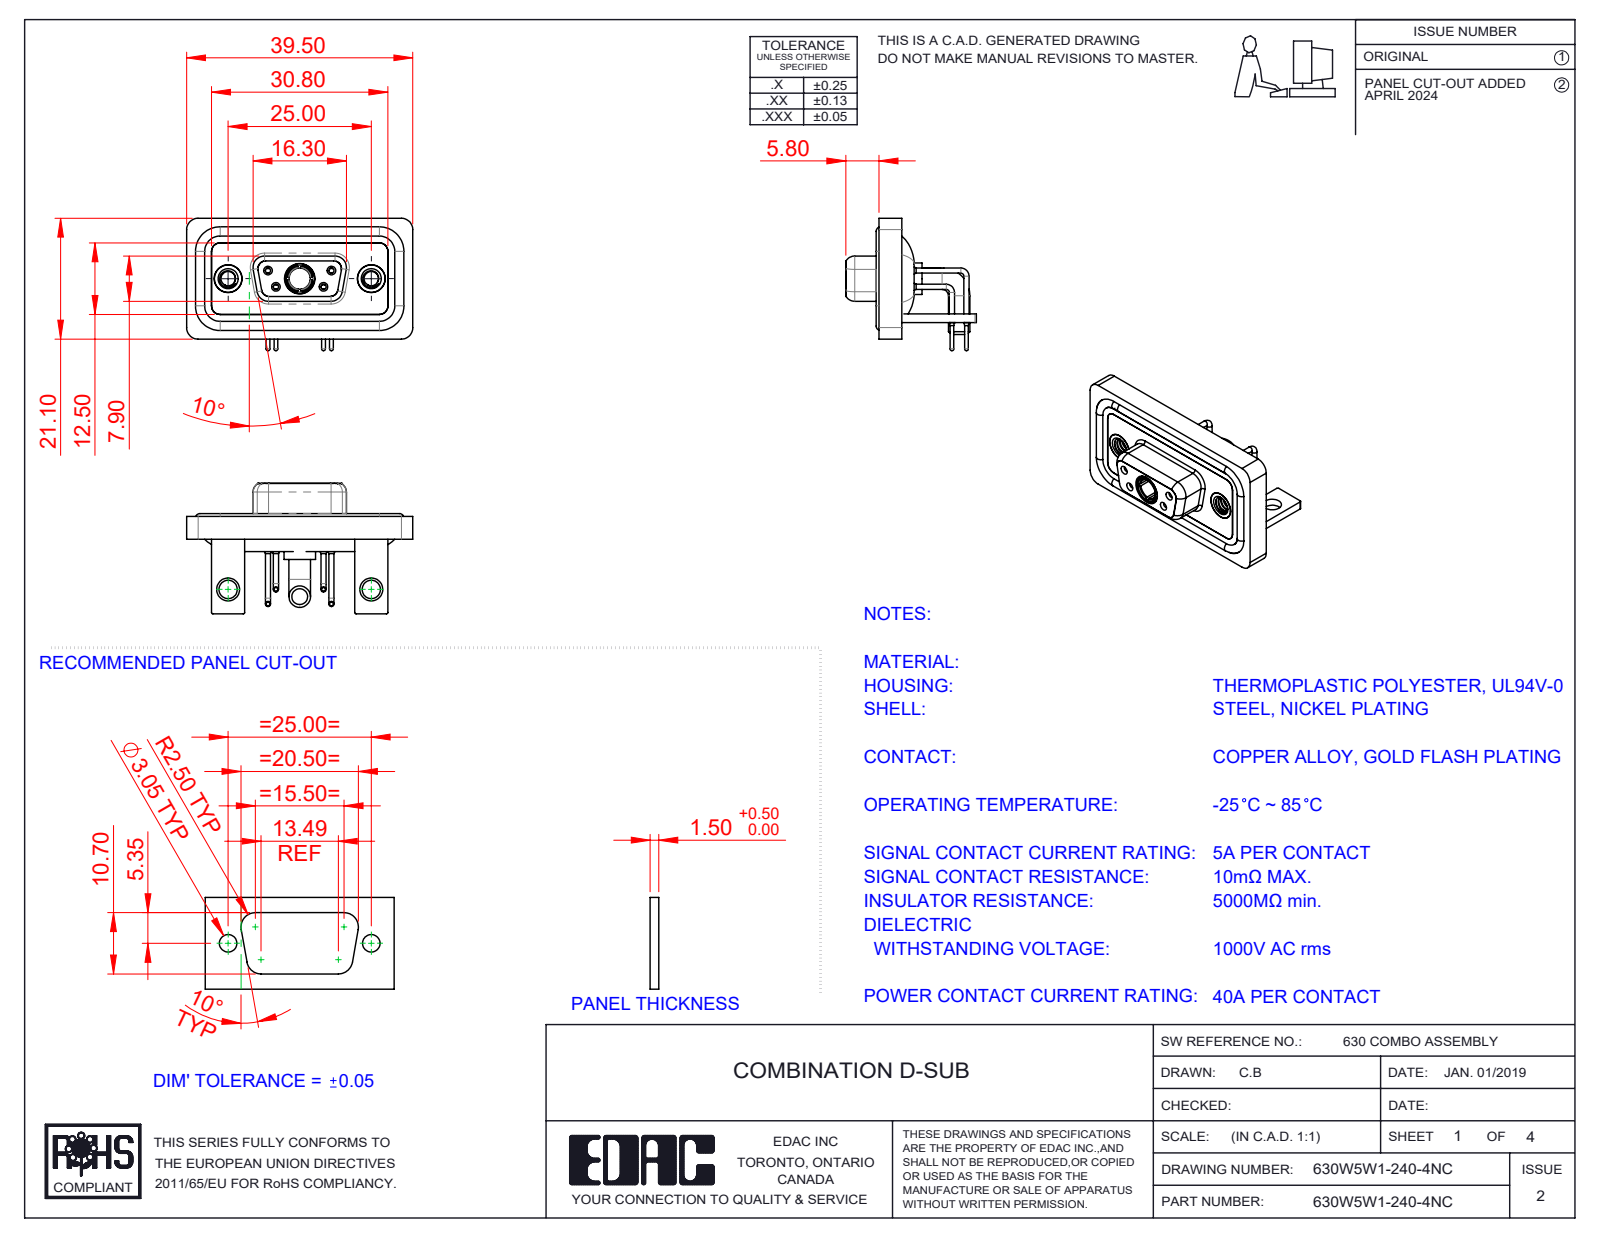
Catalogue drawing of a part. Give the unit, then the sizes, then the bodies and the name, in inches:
Units: inches
Overall size (bounding box): 1.555 × 0.91 × 0.898
Round holes (diameter × count): ⌀0.035 ×4, ⌀0.043 ×4, ⌀0.059 ×4, ⌀0.079 ×4, ⌀0.191 ×3, ⌀0.063 ×2, ⌀0.067 ×2, ⌀0.098 ×2, ⌀0.126 ×2, ⌀0.157 ×2, ⌀0.159 ×2, ⌀0.197 ×2
Round bosses / shafts (diameter × count): ⌀0.063 ×6, ⌀0.035 ×4, ⌀0.026 ×4, ⌀0.195 ×2, ⌀0.189 ×2, ⌀0.148 ×2, ⌀0.217 ×1, ⌀0.205 ×1
Partial cylindrical surfaces — rounded edges, fillets, slot ends (radius × count): R0.079 ×19, R0.059 ×18, R0.01 ×16, R0.053 ×8, R0.063 ×8, R0.02 ×5, R0.024 ×4, R0.026 ×4
Main face-to-face distances: 0.016, 0.114, 0.059, 0.071, 0.043, 0.146, 0.063, 0.031, 0.098, 0.122
Hole centre spacings: 0.124, 0.225, 0.28, 0.492, 0.713, 0.984, 0.173, 0.173
Volume: 0.321 in³ · Surface area: 13.37 in²
Bodies: 15 solids, 718 faces (214 planar, 327 cylindrical, 177 other)
Part name (STEP PRODUCT): 630Combo Contact Row 2_50 Contacts; 630Combo Threaded Rivet_A; 630Combo Shell Front_09 Contacts; 630Combo Housing_5W1 (+6 more)
STEP written by: SolidWorks 2023 (CONFIG_CONTROL_DESIGN)
